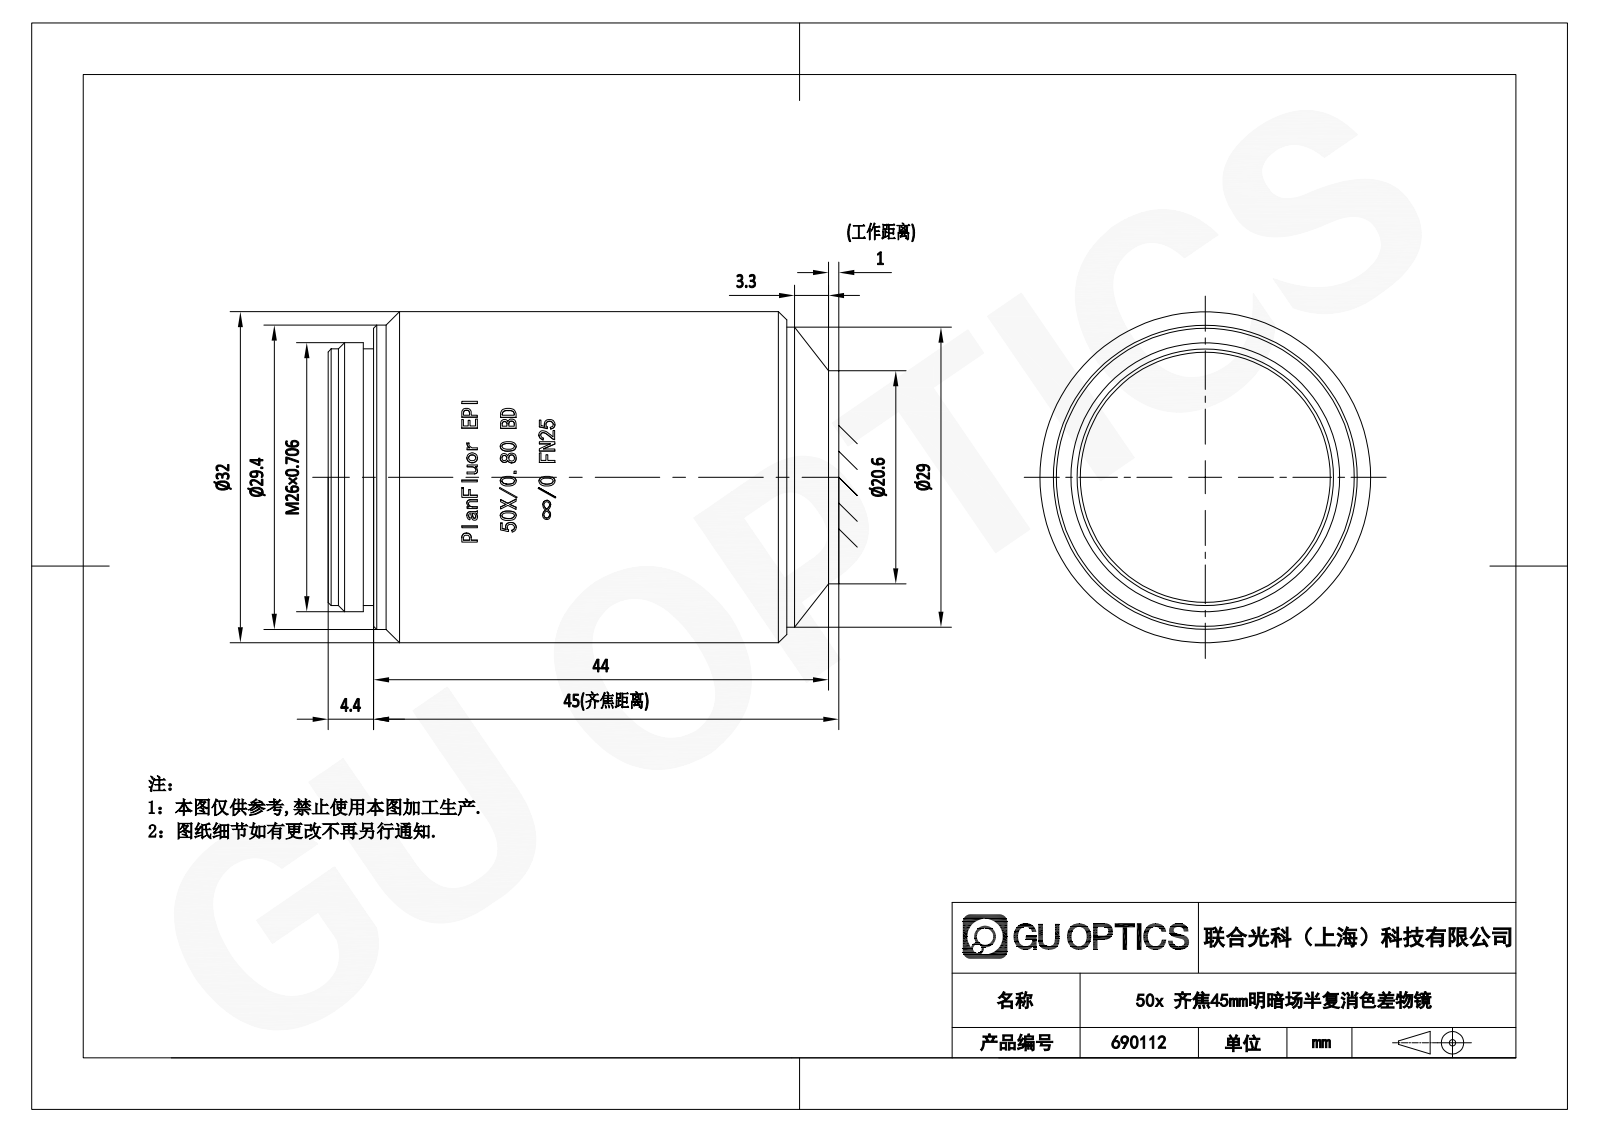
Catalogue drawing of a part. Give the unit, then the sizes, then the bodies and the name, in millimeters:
Units: millimetres
Overall size (bounding box): 48.38 × 32.05 × 32
Round bosses / shafts (diameter × count): ⌀32 ×1, ⌀29.4 ×1, ⌀29 ×1, ⌀26 ×1, ⌀24.8 ×1
Partial cylindrical surfaces — rounded edges, fillets, slot ends (radius × count): R16.05 ×1
Main face-to-face distances: 48.38, 4.4, 43.98, 44.33, 39.93, 4.05, 3.4, 1, 40.93, 44.98
Volume: 36 174 mm³ · Surface area: 6 040 mm²
Bodies: 1 solid, 338 faces (138 planar, 56 cylindrical, 144 other)
Part name (STEP PRODUCT): 690112
STEP written by: SolidWorks 2020 (CONFIG_CONTROL_DESIGN)
